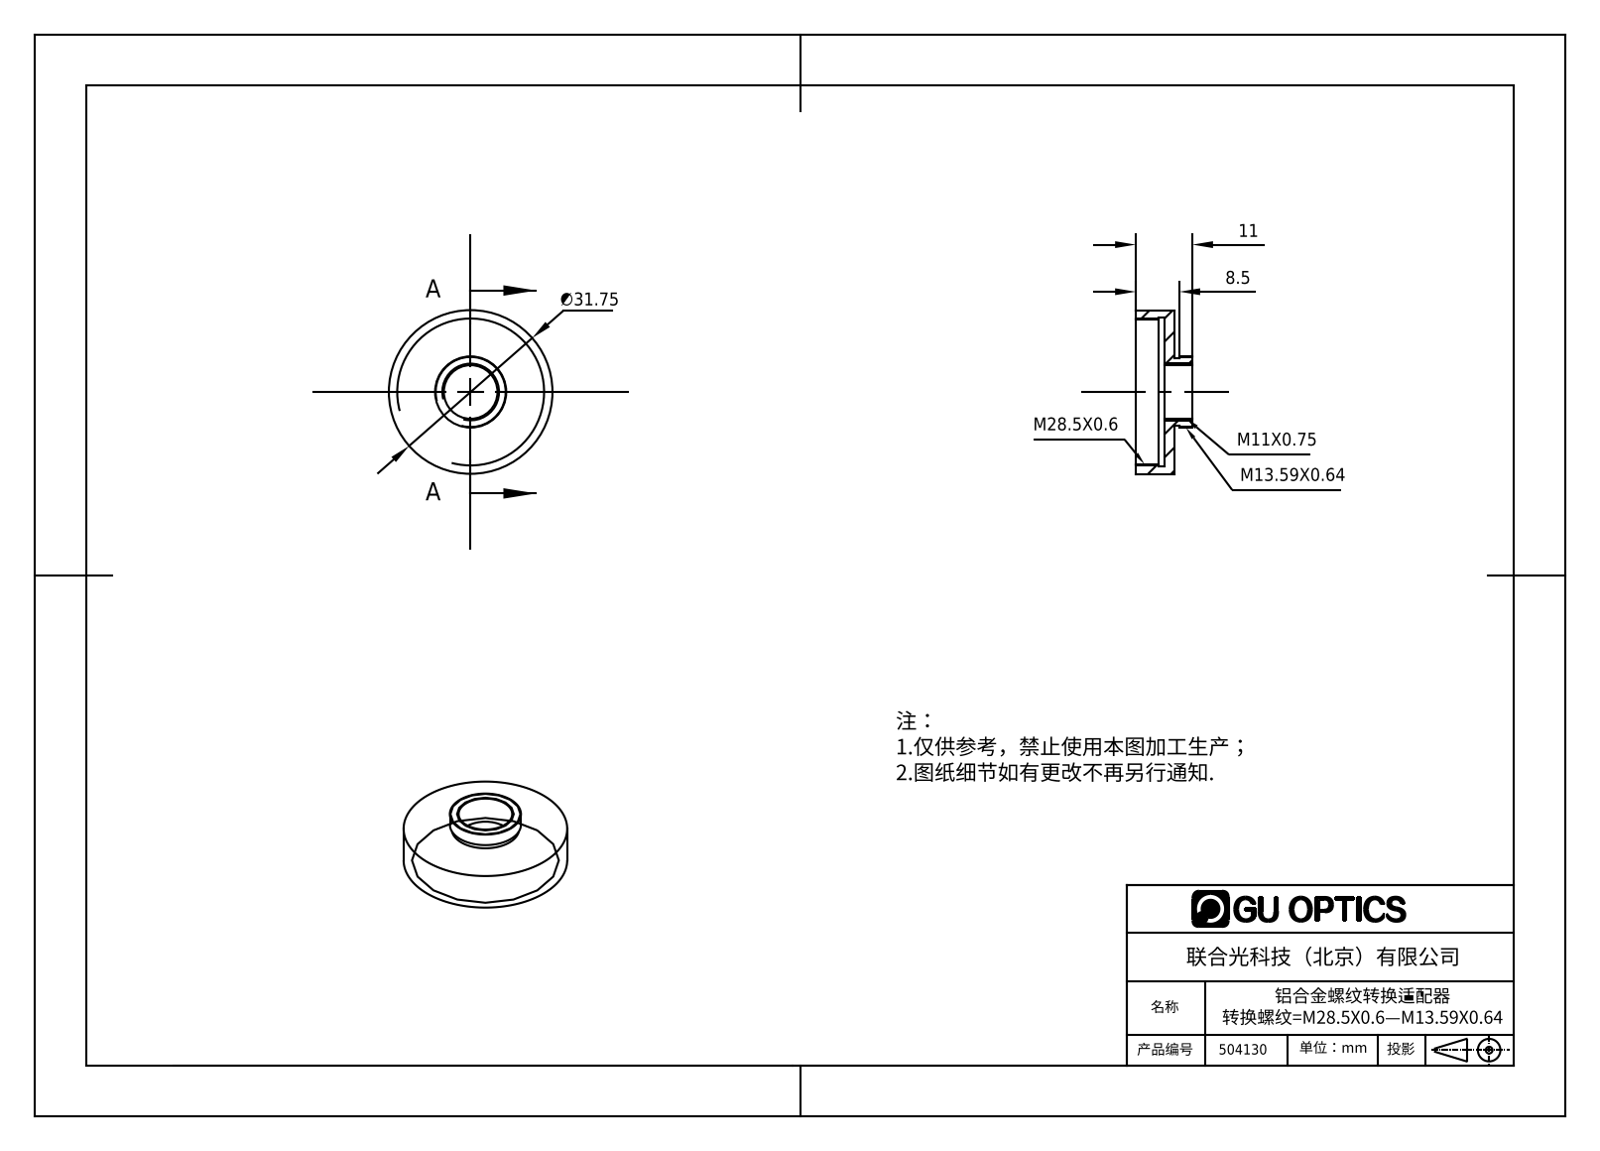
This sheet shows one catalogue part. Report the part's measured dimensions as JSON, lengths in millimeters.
{"part_name": "5041130", "step_written_by": "SolidWorks 2016 (AUTOMOTIVE_DESIGN)", "units": "millimeters", "bodies": {"solids": 1, "faces": 18, "planar": 6, "cylindrical": 12, "other": 0}, "overall_size": [31.75, 31.75, 11], "volume_mm3": 2562, "surface_area_mm2": 3069, "round_holes": [[10.4, 1], [28, 1], [28.7, 1]], "round_bosses_or_shafts": [[31.75, 1], [13.8, 1], [13.1, 1]], "face_to_face_distances": [2, 5.5, 7.5, 11, 3.5, 1, 3, 4.5, 6.5, 8.5]}
